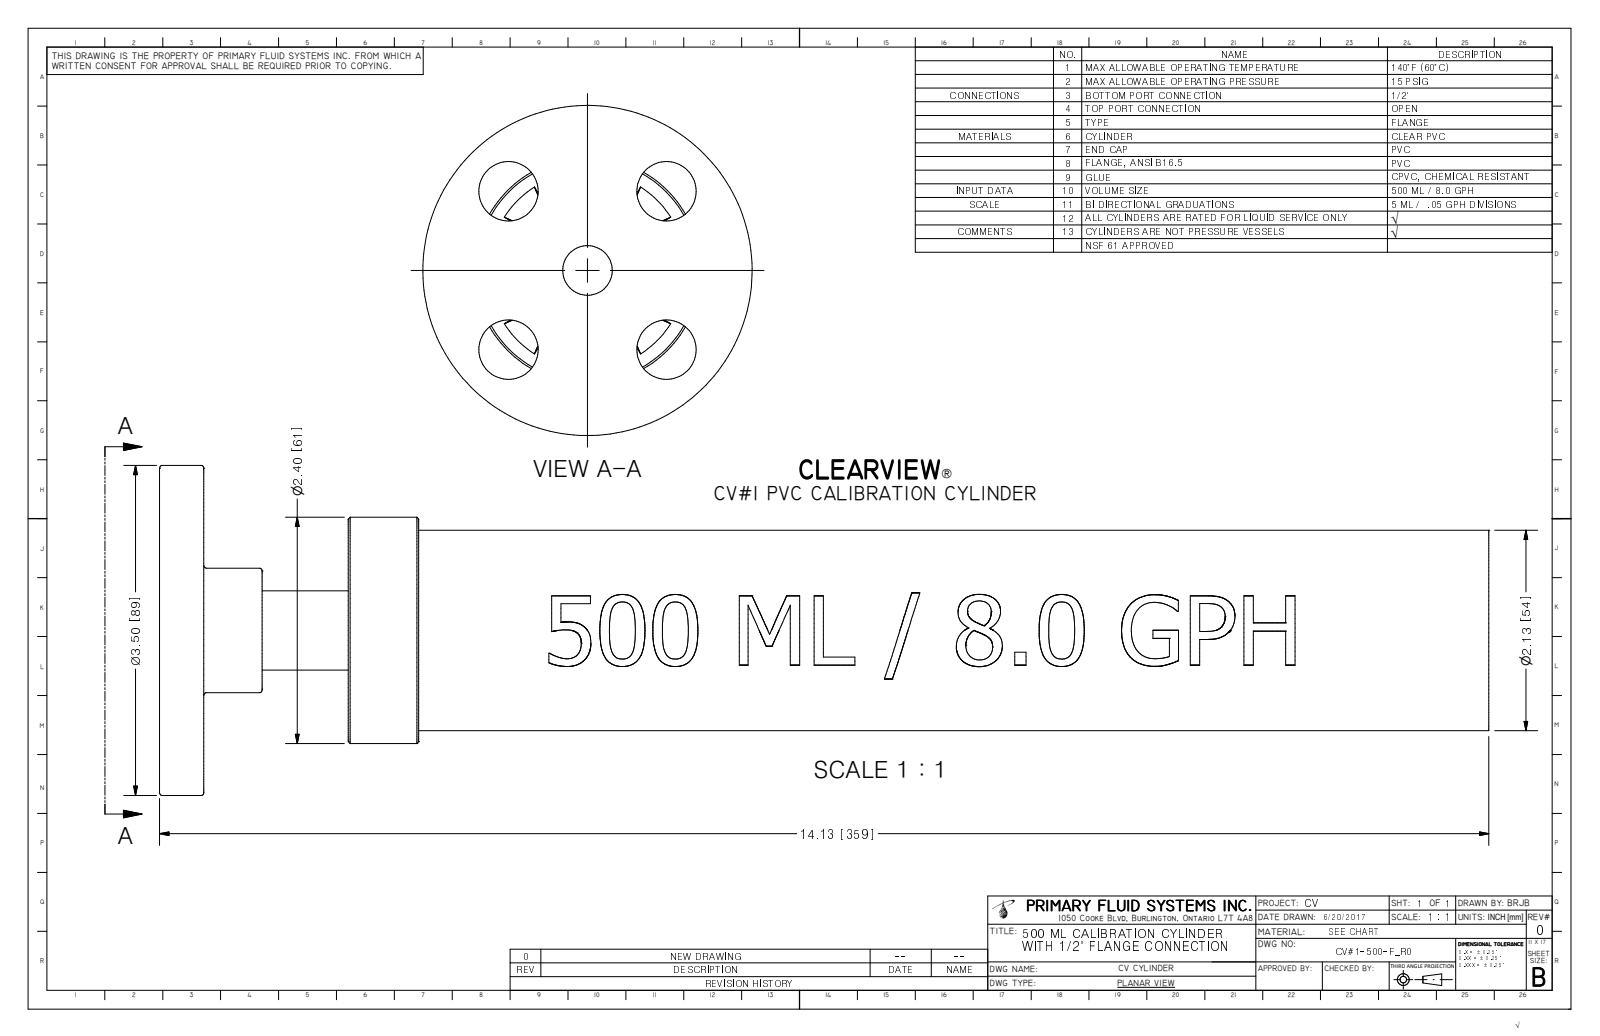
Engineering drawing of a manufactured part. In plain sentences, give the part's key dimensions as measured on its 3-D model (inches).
The part is named "PV#1-500-F_R0". Its 3-D file was written by "Autodesk Inventor 2009 (AUTOMOTIVE_DESIGN)". It is 2 solids with 249 faces: 72 planar, 28 cylindrical and 149 other. Overall it measures 14.13 by 3.5 by 3.5 inches. Its volume is 11.95 cubic inches and its surface area 212.2 square inches. Round holes: 4 of diameter 0.63, 1 of diameter 0.526, 1 of diameter 2.005. Round bosses or shafts: 1 of diameter 3.5, 1 of diameter 2.4, 1 of diameter 2.125, 1 of diameter 1.32. Partial cylindrical surfaces (rounded edges, fillets, slot ends): 1 of radius 1.061. The main face-to-face distances are 0.47, 1.09, 0.62, 14.13, 13.66, 13.04, 2.38, 1.91, 1.29, 11.75. The hole center spacings are 1.188, 1.68, 2.375.
